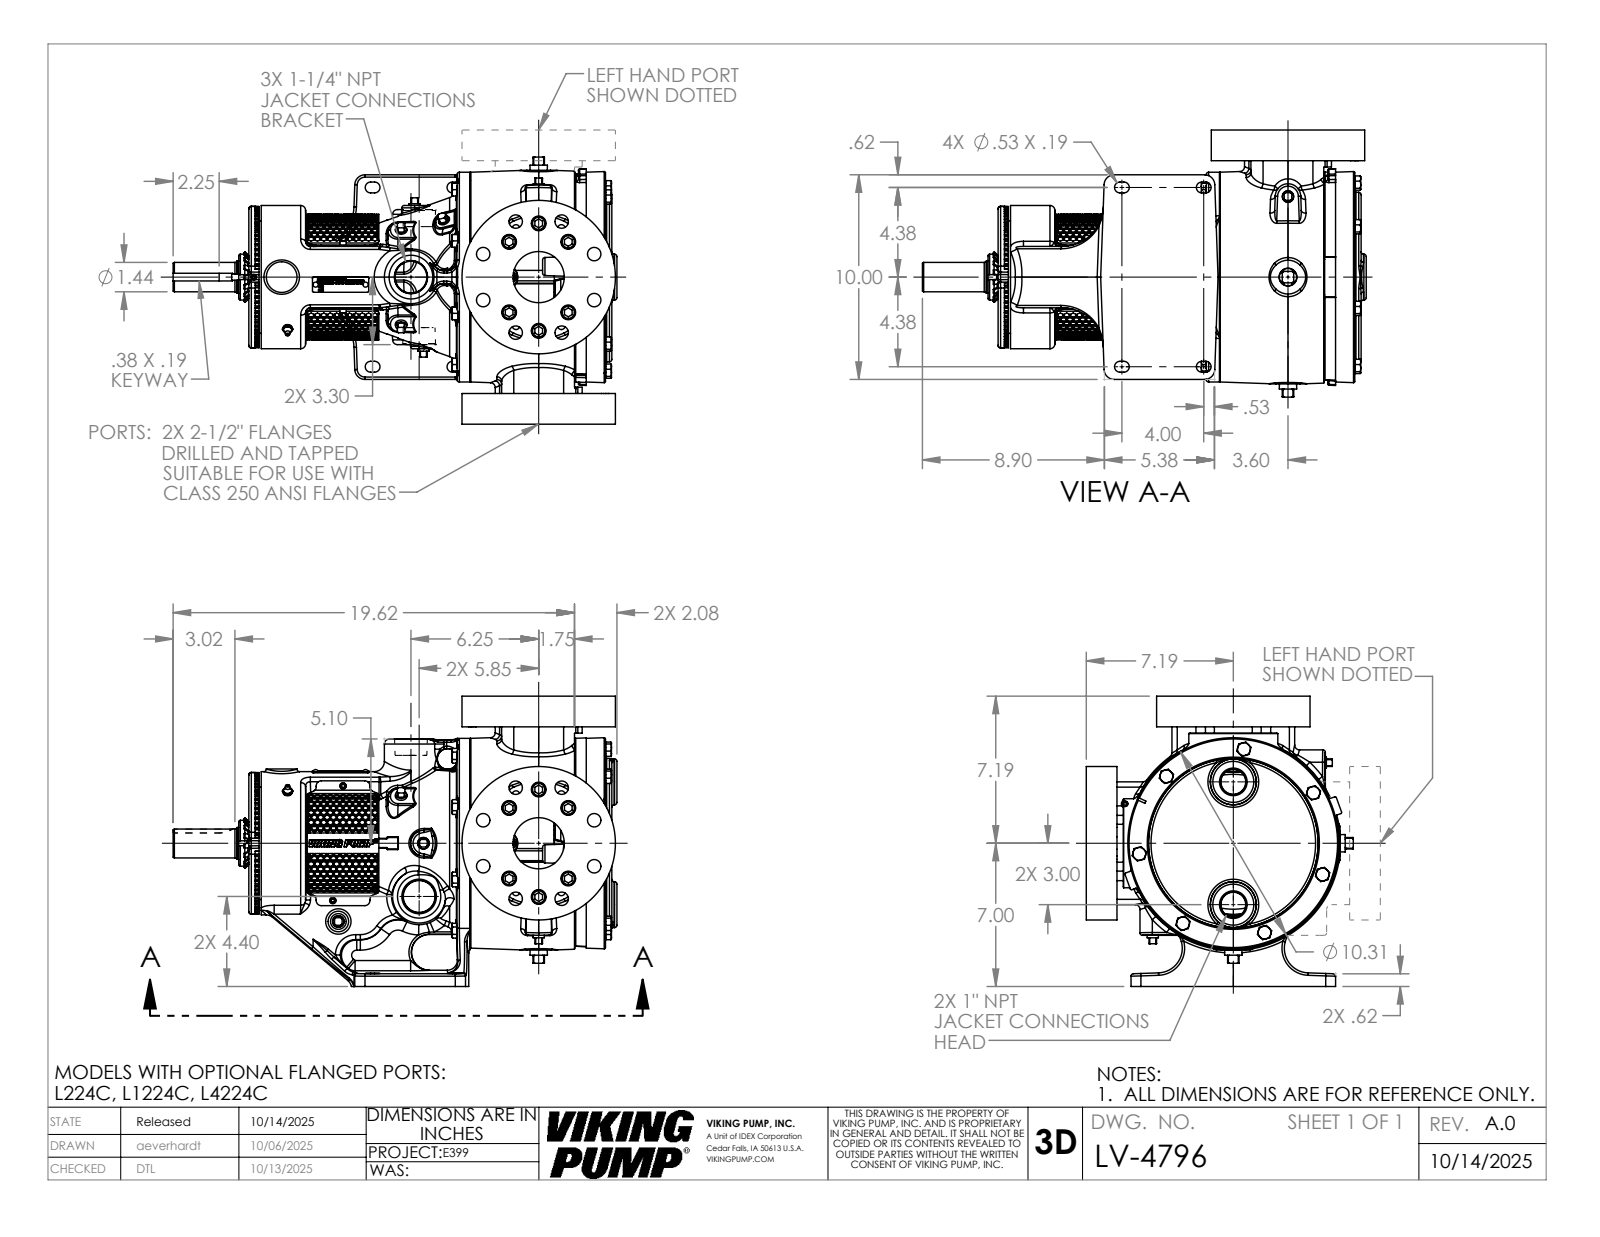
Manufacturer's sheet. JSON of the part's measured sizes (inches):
{"part_name": "LV-4796", "step_written_by": "SolidWorks 2024 (AUTOMOTIVE_DESIGN)", "units": "inches", "bodies": {"solids": 1, "faces": 4484, "planar": 1500, "cylindrical": 871, "other": 2113}, "overall_size": [21.697, 14.188, 13.053], "volume_in3": 1128, "surface_area_in2": 1432, "round_holes": [[0.656, 16], [0.719, 12], [0.25, 9], [1.094, 8], [0.199, 6], [0.159, 3], [0.266, 2], [0.313, 2], [2.5, 2], [0.453, 1], [1.577, 1], [1.593, 1]], "round_bosses_or_shafts": [[0.66, 12], [0.625, 9], [0.625, 6], [0.312, 3], [0.19, 3], [7.5, 2], [10.25, 1], [7, 1]], "partial_cylinders_radius": [[0.063, 109], [0.069, 74], [0.12, 58], [0.5, 26], [0.03, 18], [0.24, 16], [1, 16], [0.06, 13]], "face_to_face_distances": [1.5, 14.187, 0.31, 12.687, 14.687, 14.997, 3.537, 11.15, 11.46, 2.25], "hole_center_spacings": [2.248, 3, 2.937, 5.428, 1.375, 1.041, 1.402, 2.18]}
